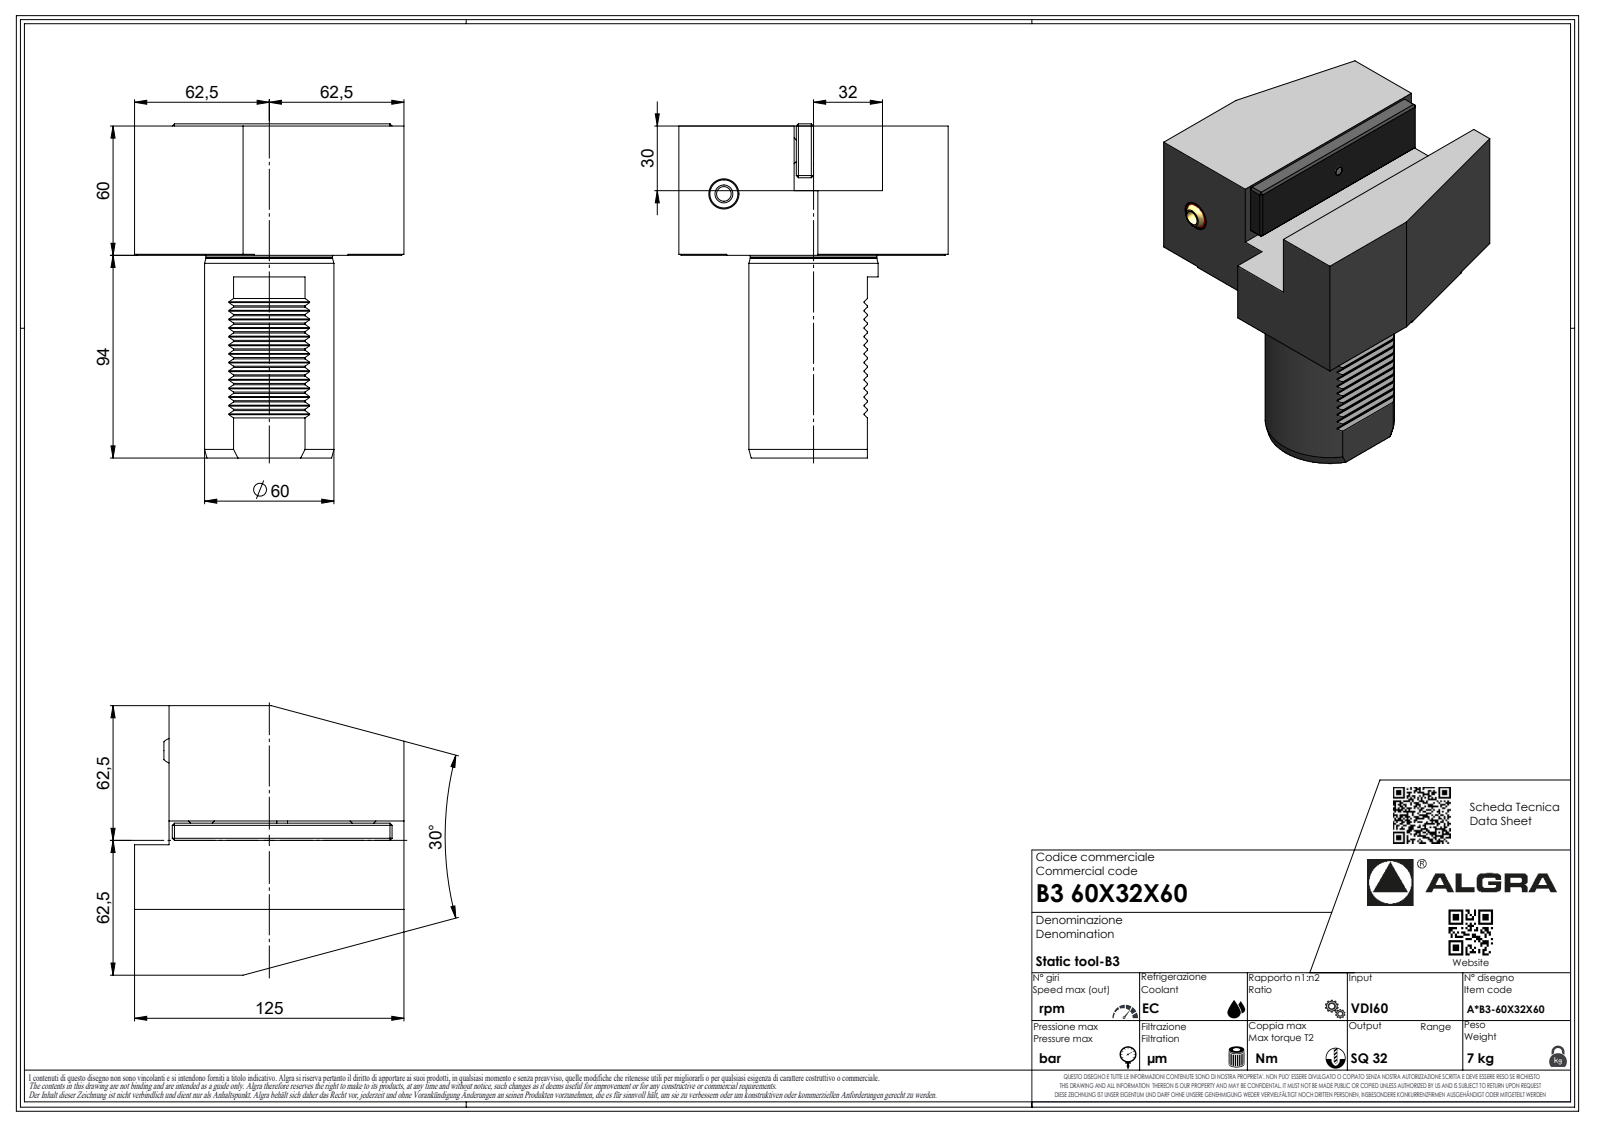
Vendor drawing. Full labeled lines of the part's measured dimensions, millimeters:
Part name (STEP PRODUCT): B360X32X60
STEP written by: SolidWorks 2023 (AUTOMOTIVE_DESIGN)
Units: millimetres
Bodies: 1 solid, 381 faces (246 planar, 45 cylindrical, 90 other)
Overall size (bounding box): 155 × 125 × 125
Volume: 927 589 mm³ · Surface area: 79 557 mm²
Round holes (diameter × count): ⌀2.1 ×1
Round bosses / shafts (diameter × count): ⌀60 ×1, ⌀58.7 ×1, ⌀6.37 ×1, ⌀1.7 ×1
Partial cylindrical surfaces — rounded edges, fillets, slot ends (radius × count): R0.3 ×14, R0.33 ×7, R0.52 ×7, R3.7 ×7, R0.21 ×1, R61.5 ×1
Main face-to-face distances: 30, 60, 125, 94.5, 62.5, 109, 30.5, 16, 94, 124
